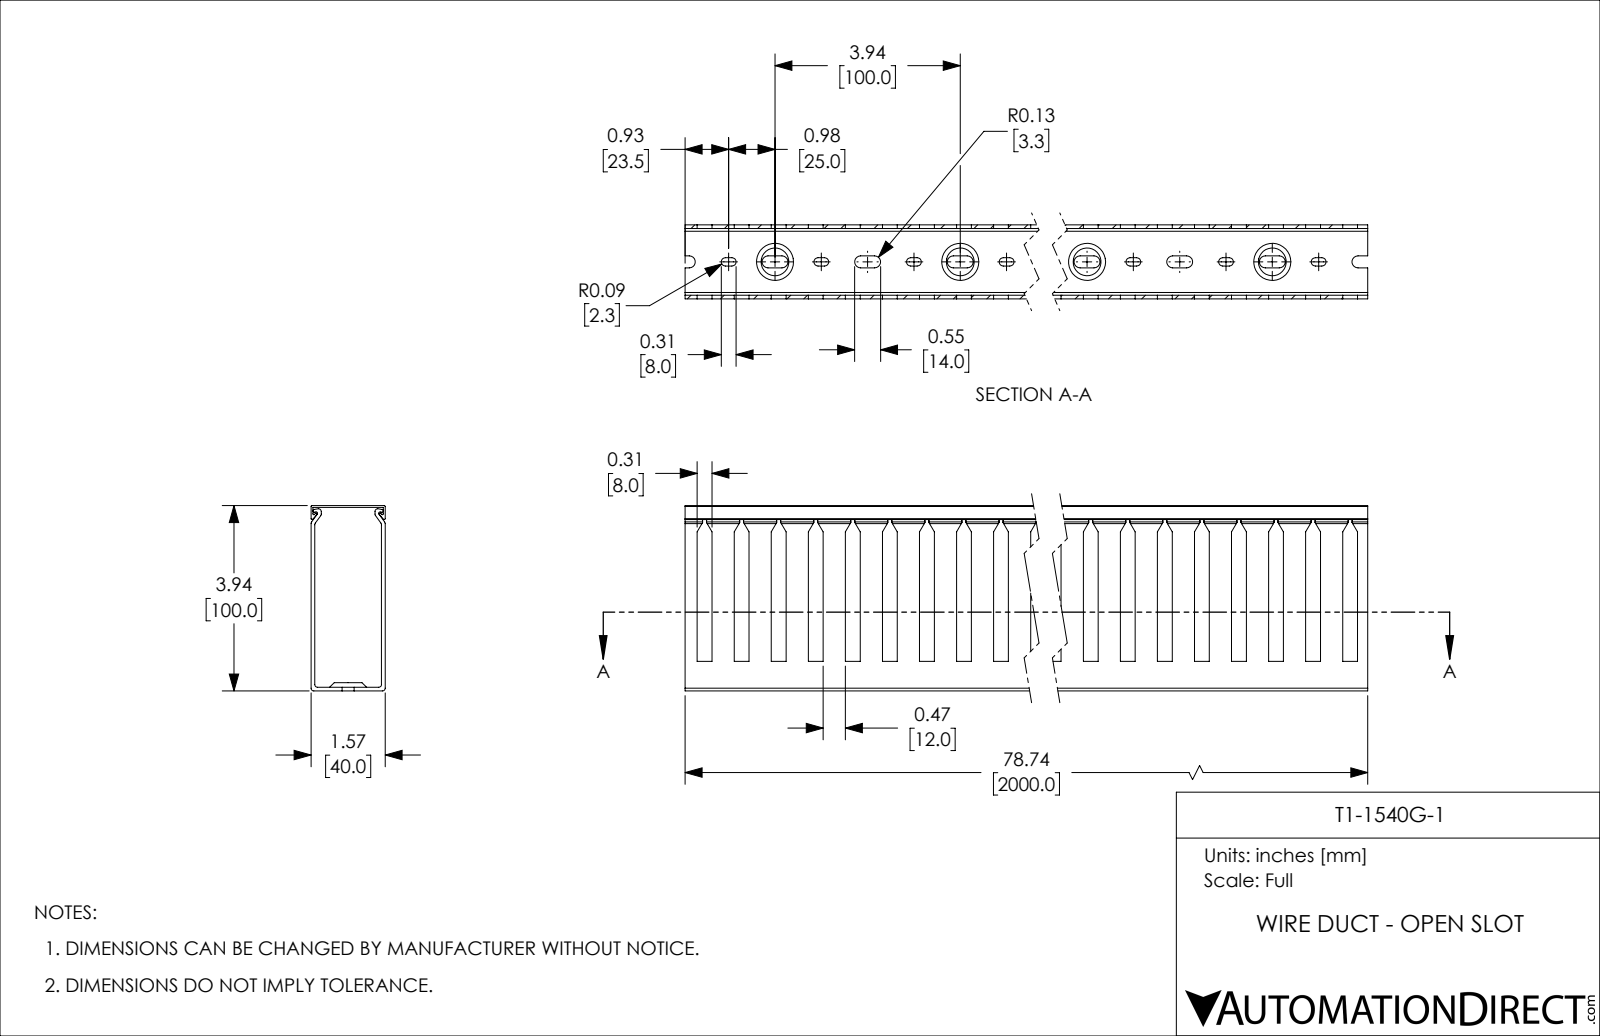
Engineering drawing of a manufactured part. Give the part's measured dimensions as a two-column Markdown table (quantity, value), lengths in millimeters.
| quantity | value |
| --- | --- |
| part name | T1-1540G-1 |
| STEP written by | SolidWorks 2021 (CONFIG_CONTROL_DESIGN) |
| units | millimeters |
| bodies | 2 solids, 1005 faces (534 planar, 431 cylindrical, 40 other) |
| overall size | 2000 × 100 × 40 |
| volume | 1 044 000 mm³ |
| surface area | 1 164 000 mm² |
| partial cylindrical surfaces (radius × count) | 2.25 × 80, 3.25 × 80, 1.5 × 12, 0.5 × 8, 0.75 × 6 |
| main face-to-face distances | 2, 38, 40, 36, 1, 100, 99, 97, 98, 39 |
